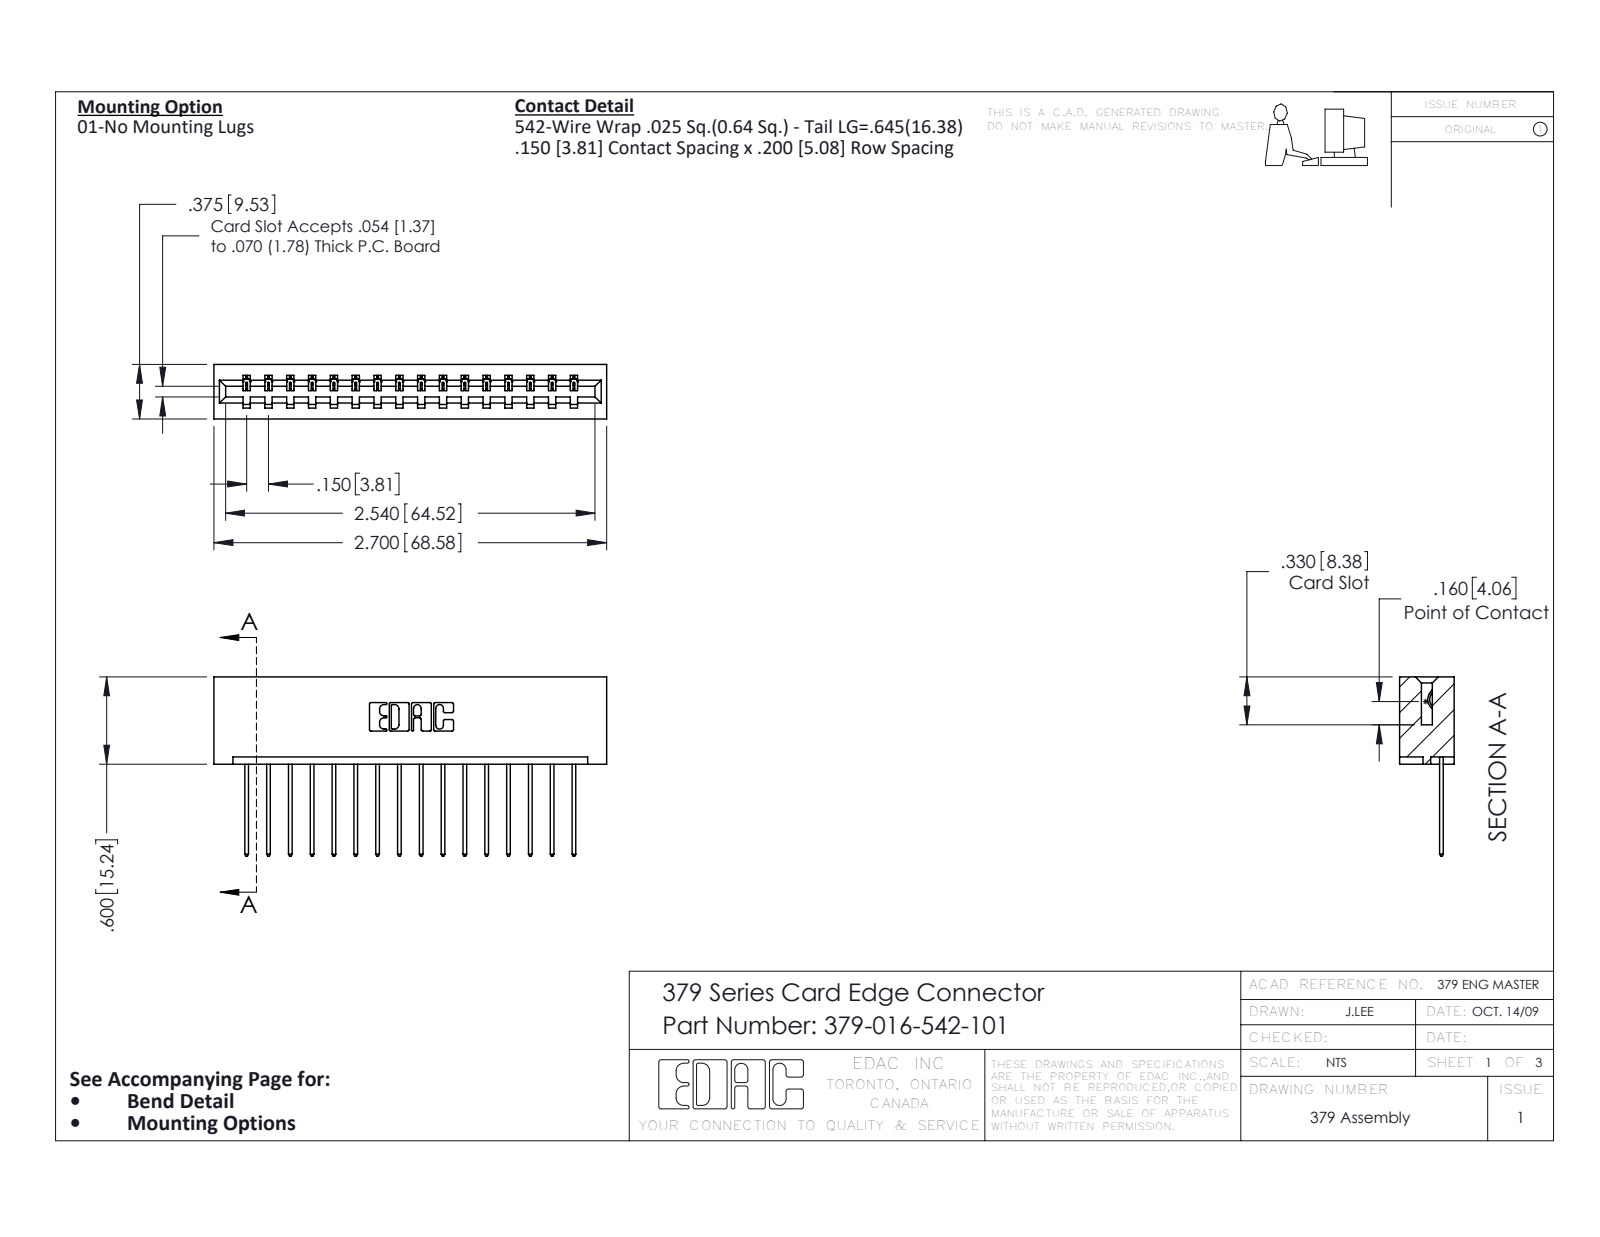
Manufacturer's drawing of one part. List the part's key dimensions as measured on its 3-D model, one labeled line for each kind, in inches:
Part name (STEP PRODUCT): 379 Part_Lugless; 379-016-542-101; 345-292-001_345-293-142
STEP written by: SolidWorks 2020 (CONFIG_CONTROL_DESIGN)
Units: inches
Bodies: 17 solids, 1034 faces (738 planar, 296 cylindrical, 0 other)
Overall size (bounding box): 2.7 × 1.232 × 0.375
Volume: 0.467 in³ · Surface area: 12.24 in²
Partial cylindrical surfaces — rounded edges, fillets, slot ends (radius × count): R0.006 ×32, R0.01 ×32, R0.01 ×22, R0.007 ×6, R0.031 ×6, R0.026 ×3, R0.014 ×1, R0.022 ×1
Main face-to-face distances: 0.3, 0.075, 0.375, 0.15, 0.6, 0.225, 0.2, 0.45, 0.1, 0.275
